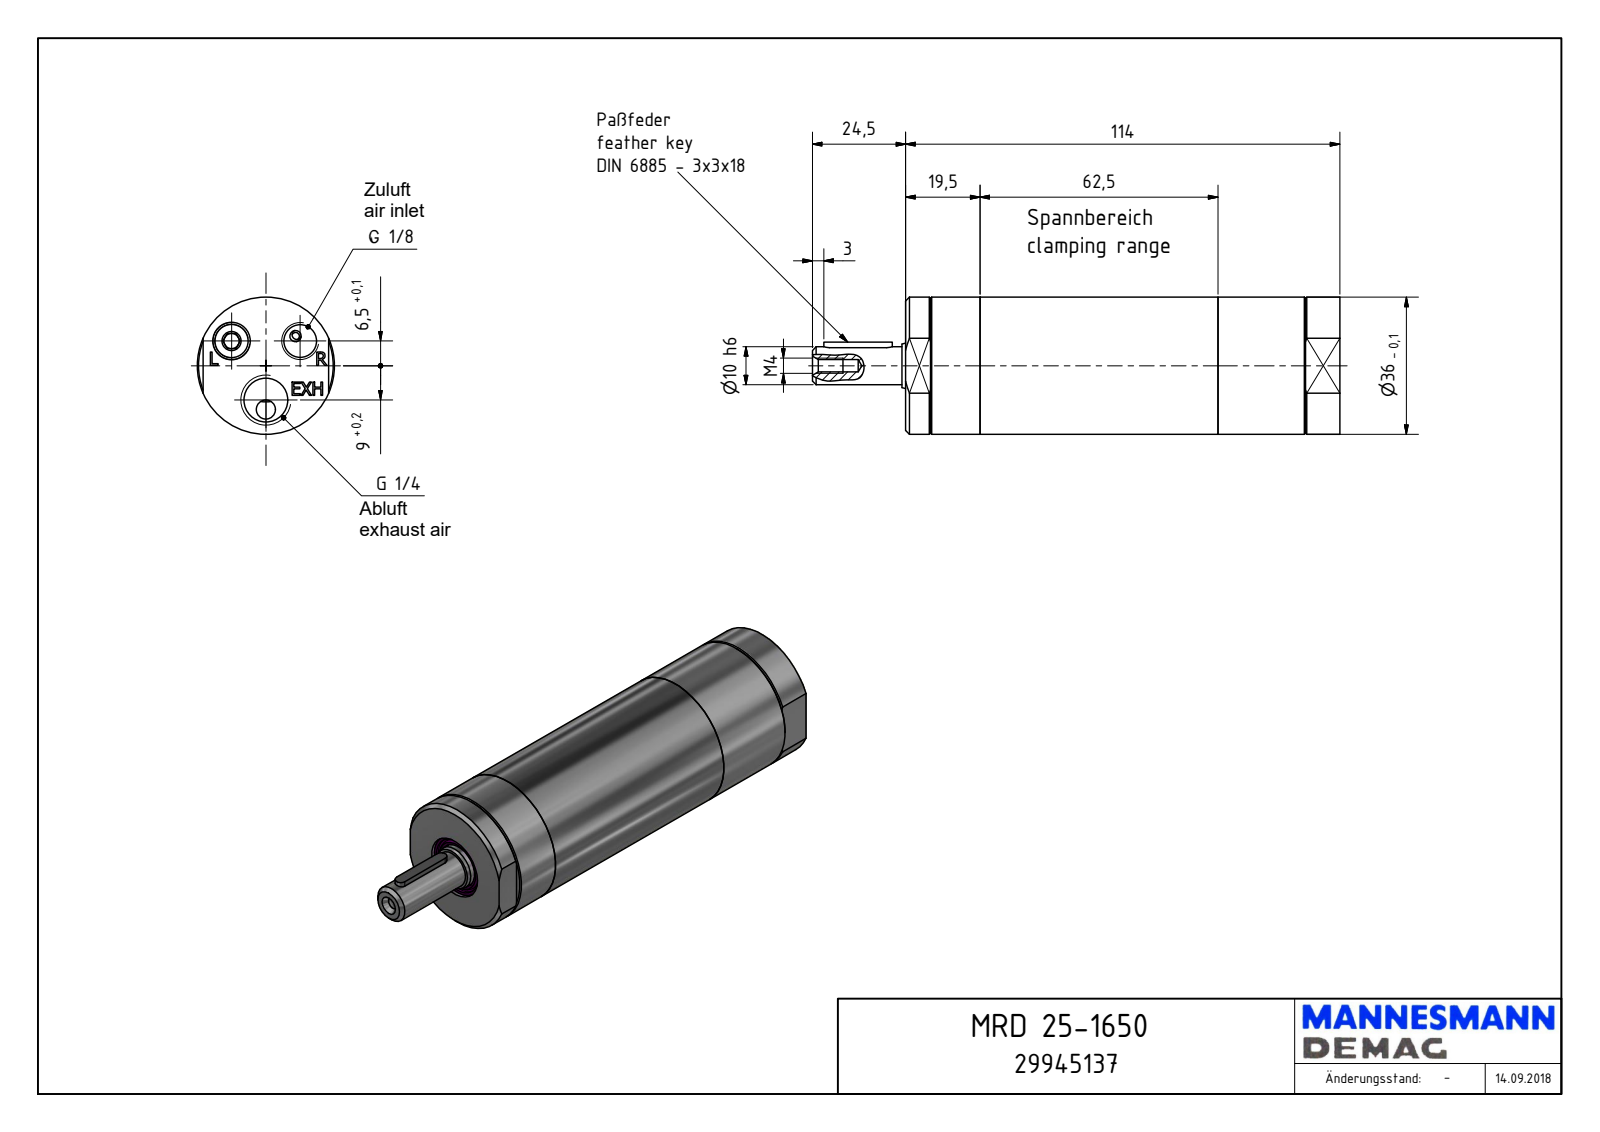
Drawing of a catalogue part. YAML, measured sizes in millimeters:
part_name: "MRD 25-1650_29945137"
step_written_by: "Autodesk Inventor 2018 (AUTOMOTIVE_DESIGN)"
units: millimeters
bodies: {solids: 1, faces: 144, planar: 94, cylindrical: 19, other: 31}
overall_size: [138.5, 36, 36]
volume: 114313
surface_area: 17433
round_holes:
  - {diameter: 8.57, count: 2}
  - {diameter: 3.24, count: 1}
  - {diameter: 4, count: 1}
  - {diameter: 5, count: 1}
  - {diameter: 11.45, count: 1}
  - {diameter: 15.5, count: 1}
  - {diameter: 17, count: 1}
round_bosses_or_shafts:
  - {diameter: 36, count: 1}
  - {diameter: 11.95, count: 1}
  - {diameter: 10, count: 1}
partial_cylinders:
  - {radius: 1.5, count: 2}
face_to_face_distances: [114, 33, 15, 98.79, 15.21, 1, 99, 106, 105, 7.21]
hole_center_spacings: [11.1, 17.92, 20.12, 2.5, 9, 11.5, 18]
